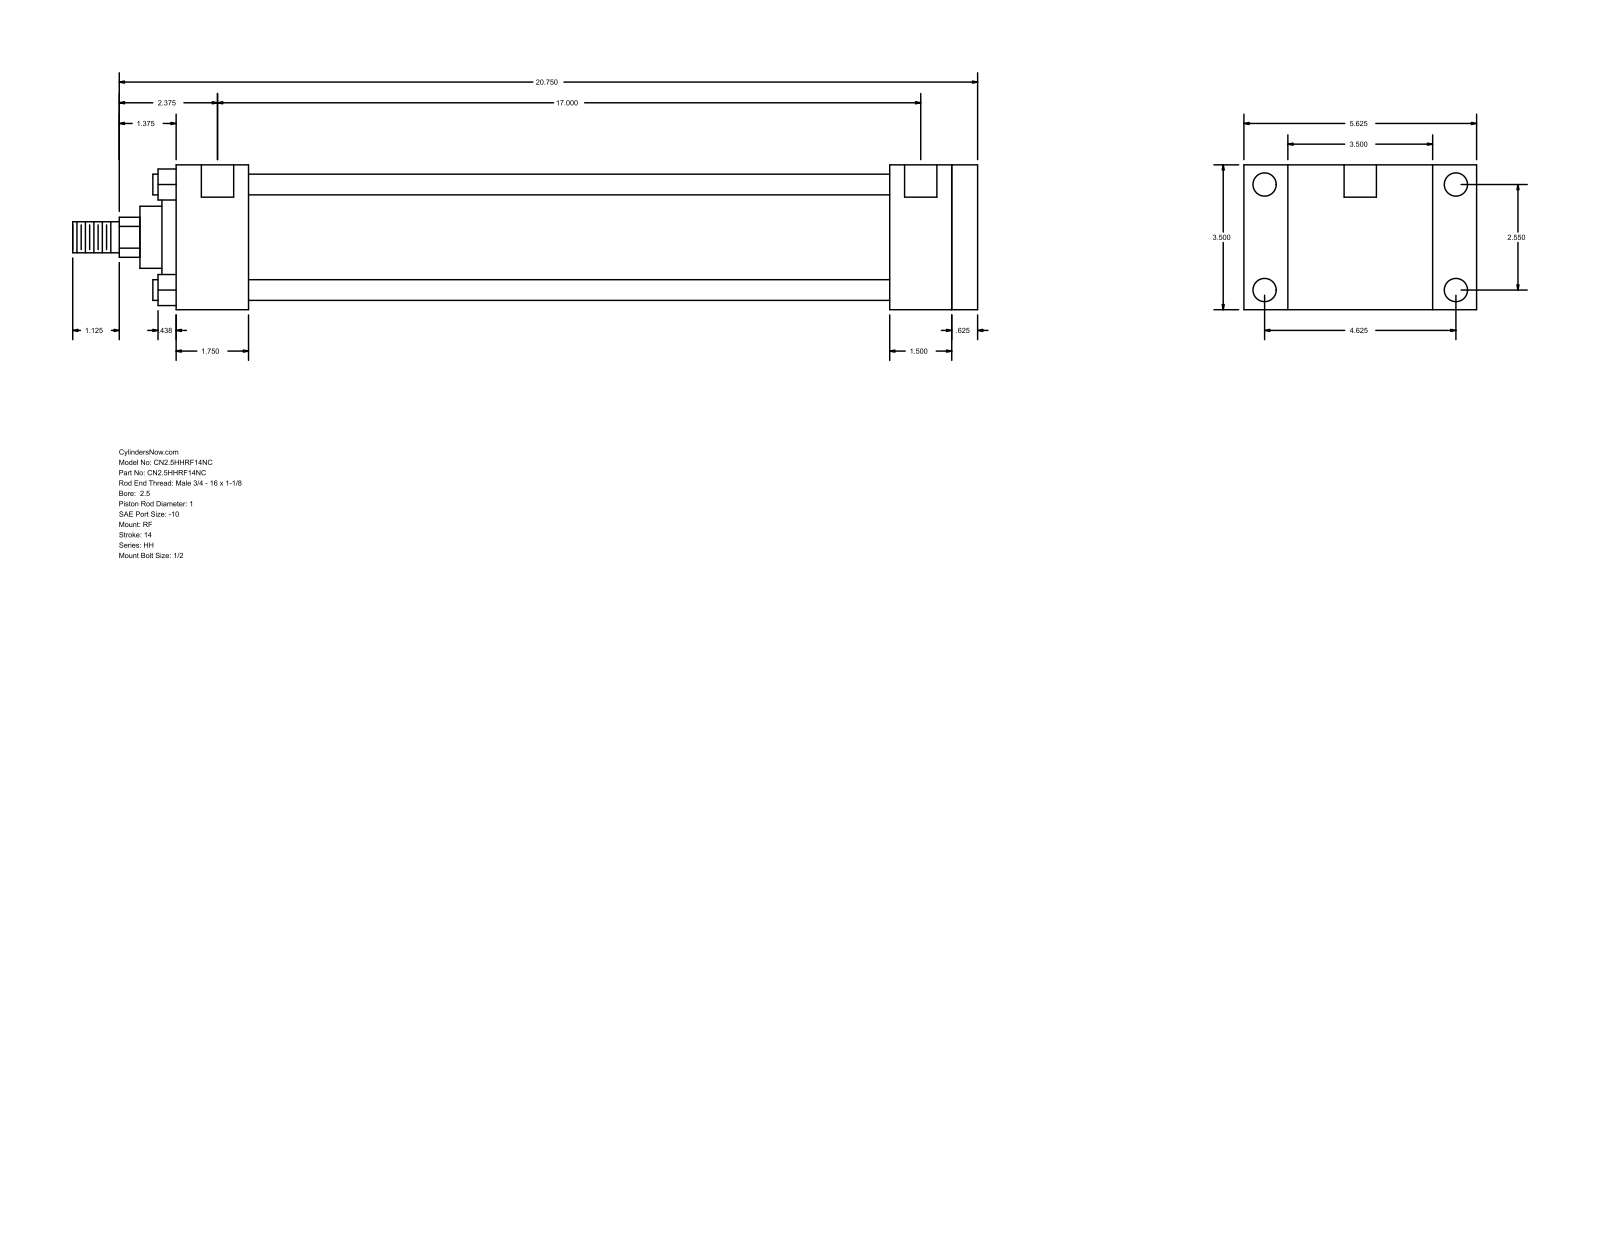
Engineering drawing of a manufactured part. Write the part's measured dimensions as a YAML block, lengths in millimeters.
part_name: "HH_RF__0250_1"
step_written_by: "GSSL Pune (CONFIG_CONTROL_DESIGN)"
units: millimeters
bodies: {solids: 0, faces: 94, planar: 65, cylindrical: 29, other: 0}
overall_size: [555.62, 142.88, 88.9]
round_holes:
  - {diameter: 5.56, count: 4}
  - {diameter: 14.3, count: 4}
  - {diameter: 19.84, count: 2}
round_bosses_or_shafts:
  - {diameter: 12.7, count: 4}
  - {diameter: 73.03, count: 1}
  - {diameter: 60.33, count: 1}
  - {diameter: 38.1, count: 1}
  - {diameter: 25.4, count: 1}
  - {diameter: 19.05, count: 1}
partial_cylinders:
  - {radius: 12.29, count: 1}
face_to_face_distances: [88.9, 15.87, 476.26, 492.13, 44.46, 431.8, 447.67, 438.15, 393.69, 38.11]
hole_center_spacings: [1.59, 64.76, 117.48, 134.15, 433.38, 434.97, 431.79]
